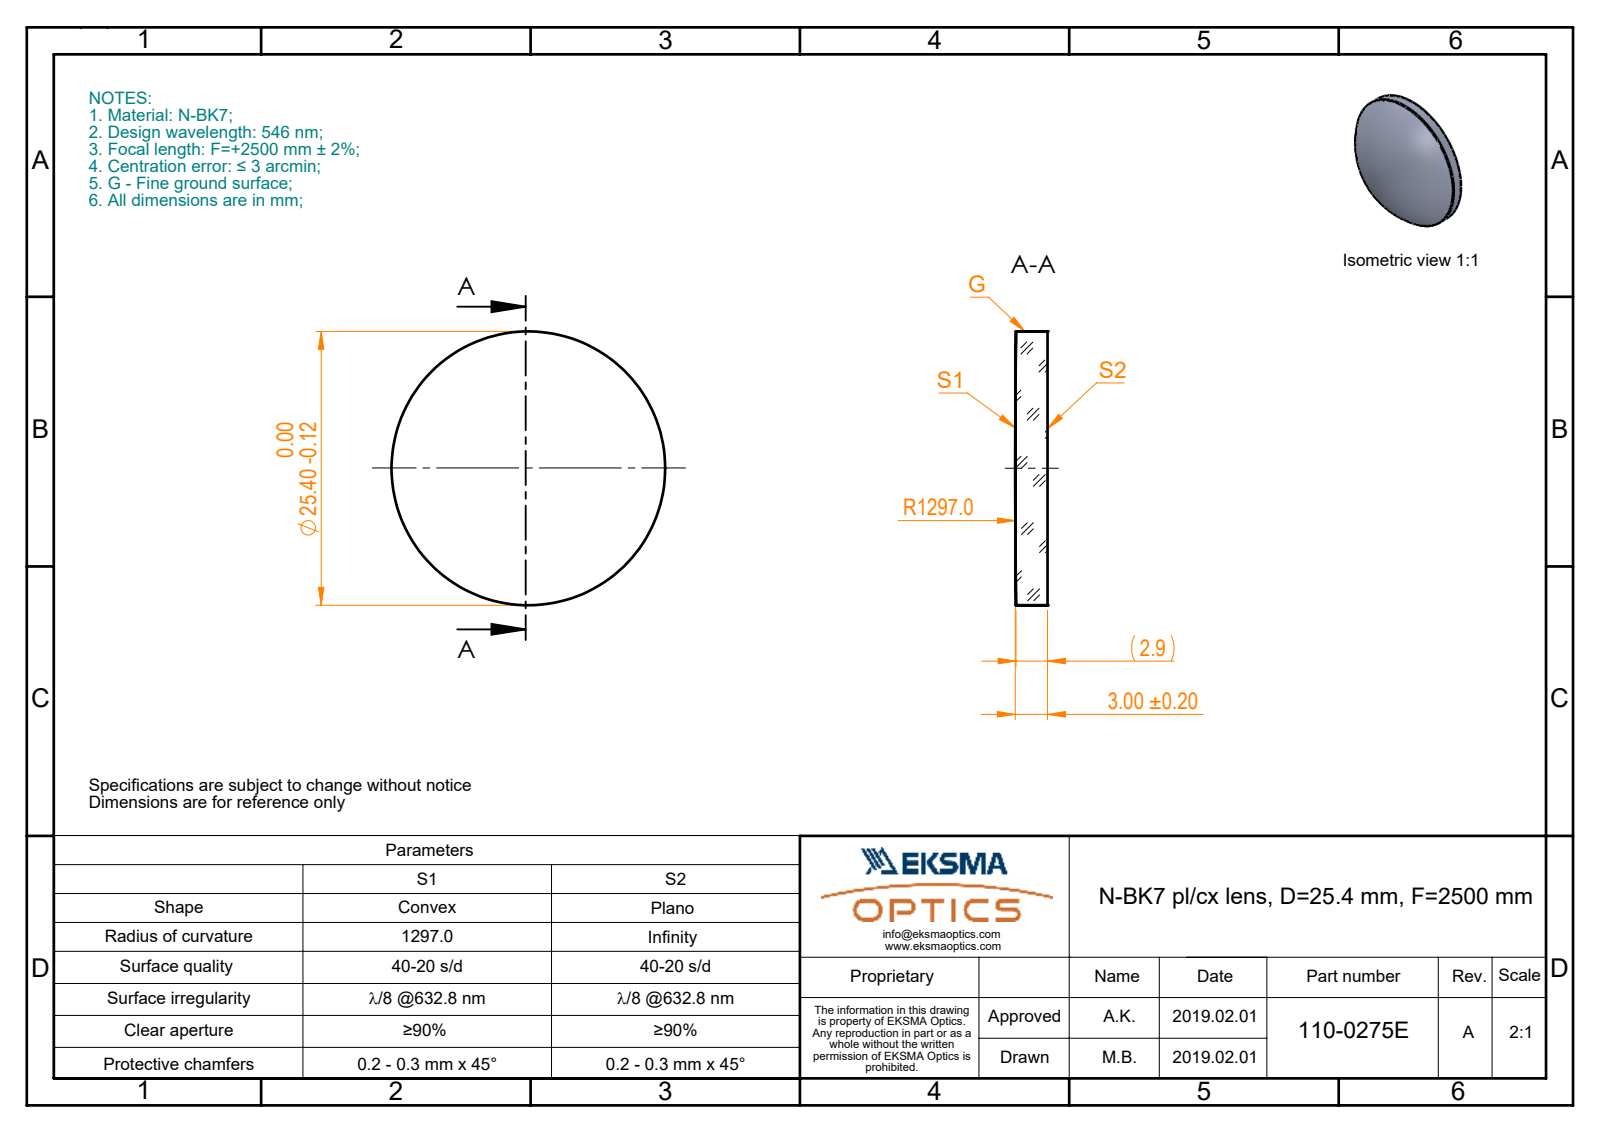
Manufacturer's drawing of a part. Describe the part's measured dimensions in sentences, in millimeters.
The part is named "110-0275E BK7 pl-cx 25.4 F2500". Its 3-D file was written by "SolidWorks 2017 (CONFIG_CONTROL_DESIGN)". It is 1 solid with 5 faces: 1 planar, 2 cylindrical and 2 other. Overall it measures 25.4 by 25.4 by 3 millimeters. Its volume is 1 504 cubic millimeters and its surface area 1 248 square millimeters. Round bosses or shafts: 1 of diameter 25.4.
